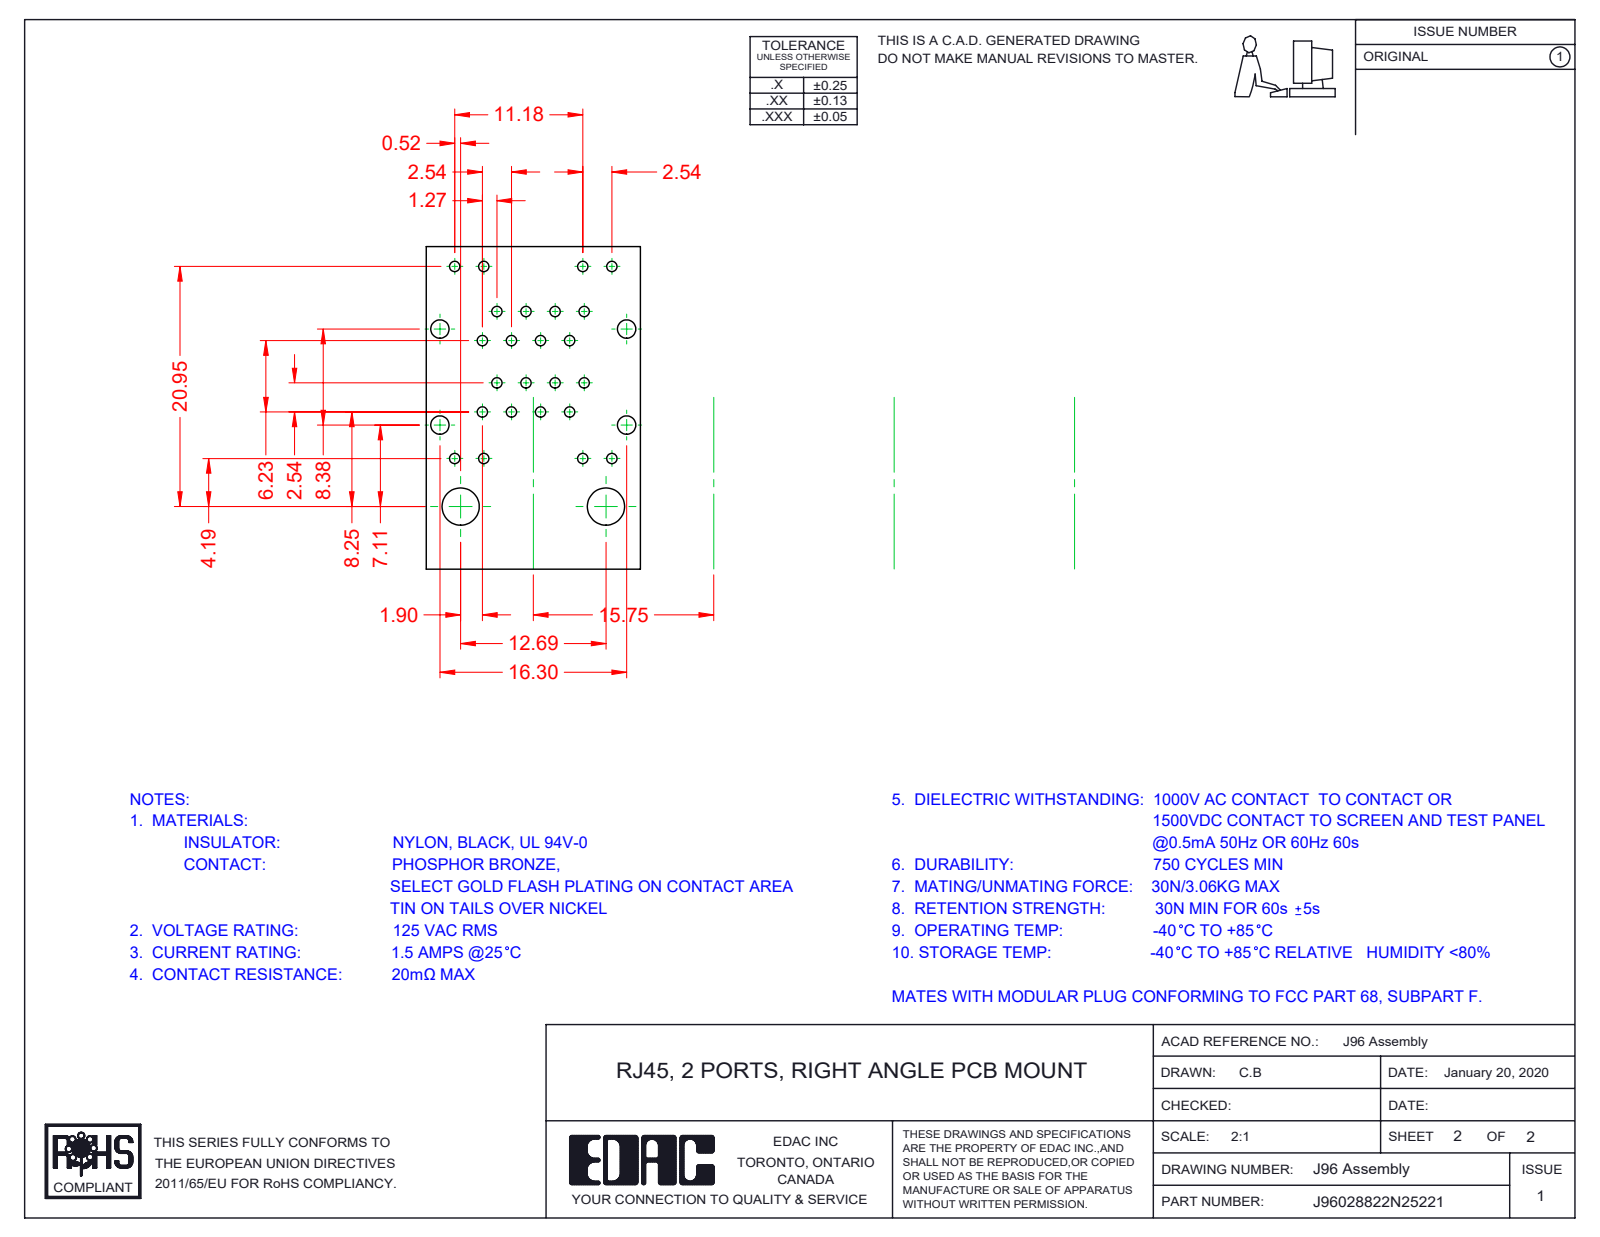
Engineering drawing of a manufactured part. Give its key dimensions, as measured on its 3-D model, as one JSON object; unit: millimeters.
{"part_name": "96 Contacts Upper; 96 Shield_2 Ports LED - EMI; 96 Contact Lock Lower; 96 LED RH Lower_5-Green-Yellow (+8 more)", "step_written_by": "SolidWorks 2016 (CONFIG_CONTROL_DESIGN)", "units": "millimeters", "bodies": {"solids": 27, "faces": 2421, "planar": 1865, "cylindrical": 450, "other": 106}, "overall_size": [31.38, 28.68, 16.8], "volume_mm3": 6849, "surface_area_mm2": 19094, "partial_cylinders_radius": [[0.25, 48], [0.15, 32], [0.35, 24], [0.5, 16], [1, 16], [0.2, 14], [0.7, 9], [2, 5]], "face_to_face_distances": [16.3, 16.1, 1.75, 16.5, 14.75, 1.55, 14.55, 0.53, 1.48, 11.2]}
